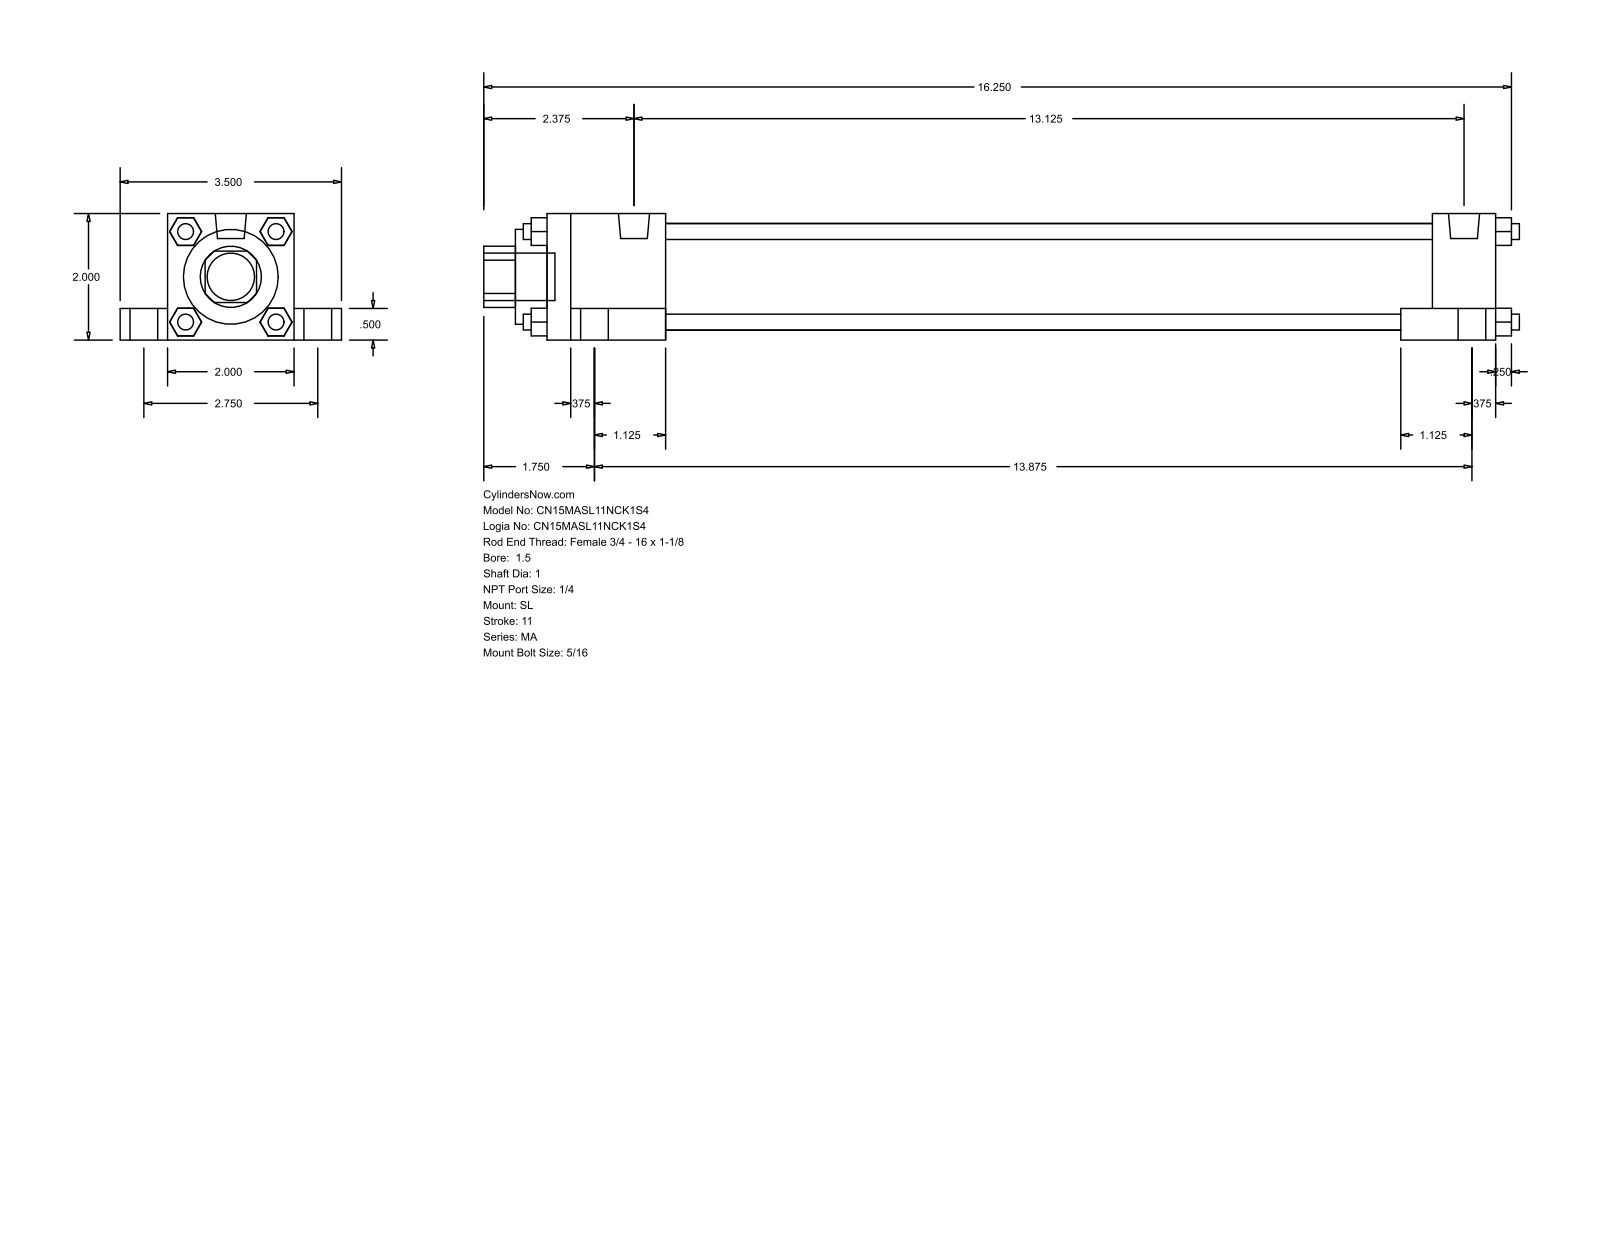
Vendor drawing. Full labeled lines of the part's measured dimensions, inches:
Part name (STEP PRODUCT): MA_SL__0150_1
STEP written by: GSSL Pune (CONFIG_CONTROL_DESIGN)
Units: inches
Bodies: 0 solids, 148 faces (112 planar, 36 cylindrical, 0 other)
Overall size (bounding box): 16.375 × 3.5 × 2
Round holes (diameter × count): ⌀1 ×1, ⌀1.5 ×1, ⌀1.69 ×1
Round bosses / shafts (diameter × count): ⌀0.687 ×4, ⌀0.437 ×4, ⌀0.313 ×4, ⌀0.25 ×4, ⌀0.492 ×2, ⌀0.75 ×1
Partial cylindrical surfaces — rounded edges, fillets, slot ends (radius × count): R0.484 ×1
Main face-to-face distances: 2, 0.5, 0.75, 2.75, 0.375, 1.5, 0.25, 15, 1, 14
